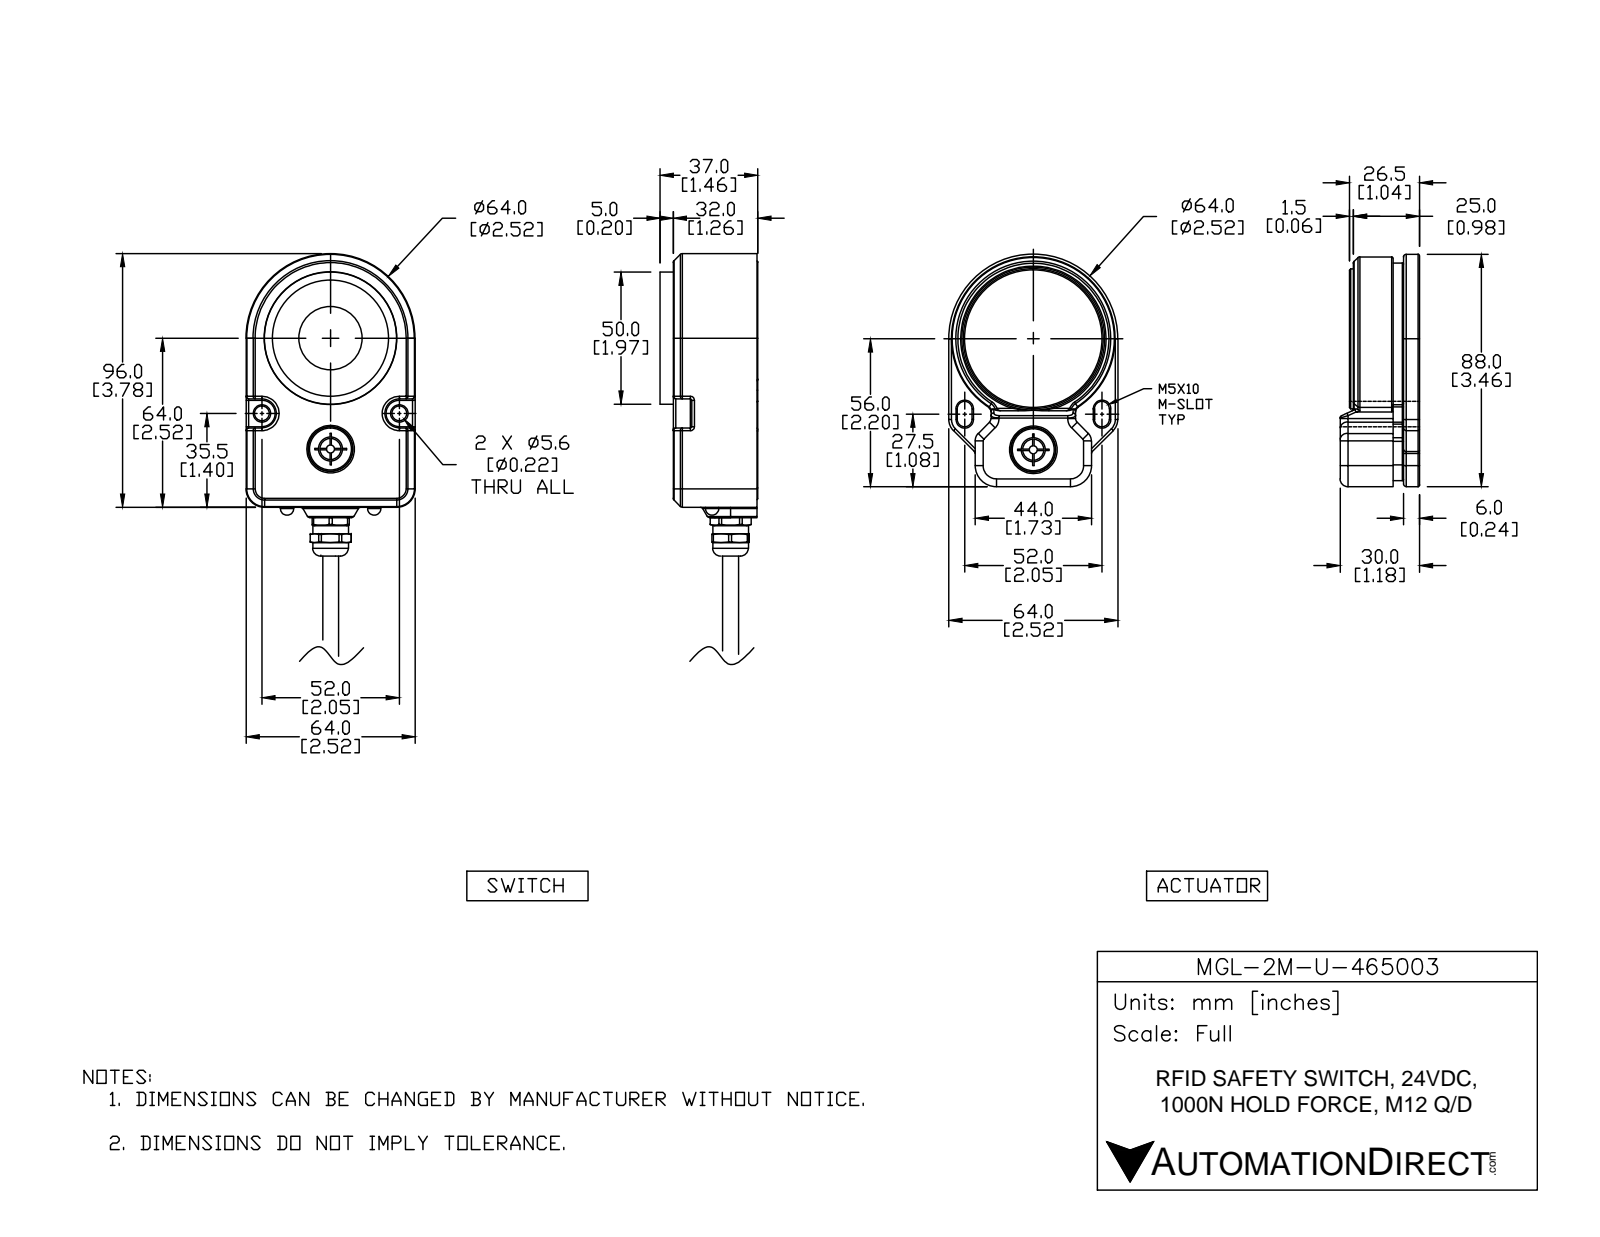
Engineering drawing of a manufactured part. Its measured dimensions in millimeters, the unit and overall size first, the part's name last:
Units: millimetres
Overall size (bounding box): 196 × 64.5 × 64
Round holes (diameter × count): ⌀2.5 ×8, ⌀4 ×8, ⌀3.3 ×6, ⌀8 ×6, ⌀5 ×5, ⌀8.2 ×3, ⌀5.6 ×2, ⌀9 ×2, ⌀9.5 ×2, ⌀10.5 ×2, ⌀17 ×2, ⌀6.4 ×1
Round bosses / shafts (diameter × count): ⌀0.5 ×4, ⌀2 ×3, ⌀6 ×2, ⌀5.8 ×2, ⌀5.4 ×2, ⌀62 ×1, ⌀57.4 ×1, ⌀53 ×1
Partial cylindrical surfaces — rounded edges, fillets, slot ends (radius × count): R0.5 ×216, R1 ×87, R2 ×30, R0.3 ×17, R3 ×15, R4 ×9, R0.6 ×7, R4.5 ×6
Main face-to-face distances: 6, 10.5, 3, 19, 48, 58.5, 26.5, 10, 9, 29
Hole centre spacings: 17.9, 19.5, 27.6, 26, 8.8, 9.6, 9.7, 9.8
Volume: 203 500 mm³ · Surface area: 109 400 mm²
Bodies: 20 solids, 1852 faces (454 planar, 786 cylindrical, 612 other)
Part name (STEP PRODUCT): MGL-2M-U-465003_1; MGL-2M-U-465003; MGL-2M-U-465003_2
STEP written by: SolidWorks 2017 (AUTOMOTIVE_DESIGN)
